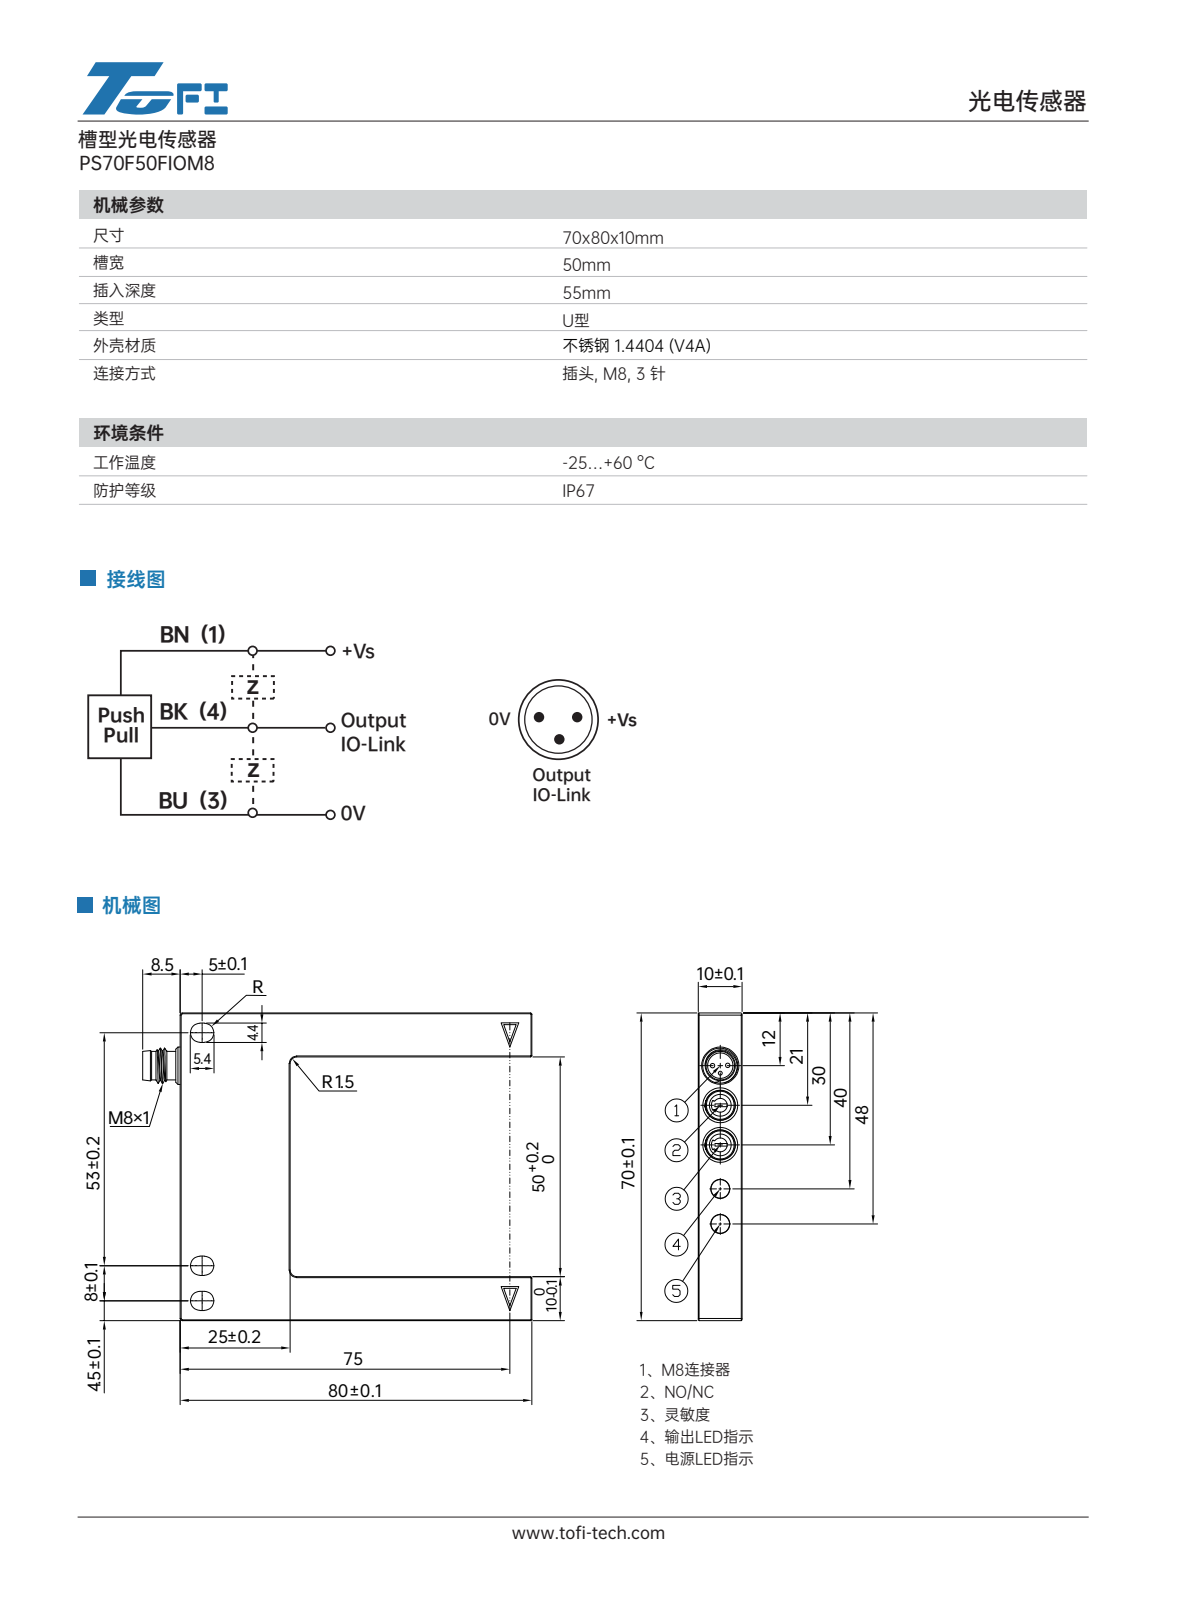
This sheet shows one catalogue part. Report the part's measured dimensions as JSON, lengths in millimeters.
{"part_name": "P70-CP", "step_written_by": "SolidWorks 2016 (CONFIG_CONTROL_DESIGN)", "units": "millimeters", "bodies": {"solids": 0, "faces": 776, "planar": 346, "cylindrical": 232, "other": 198}, "overall_size": [88.5, 70, 10], "round_holes": [[8, 3], [4.33, 2], [5, 2], [5.9, 2], [7.1, 2], [4.04, 1], [5.04, 1], [5.1, 1], [5.8, 1], [5.85, 1], [6.85, 1], [6.9, 1]], "round_bosses_or_shafts": [[0.5, 6], [1, 3], [6.8, 2], [4.3, 2], [2.7, 2], [9, 1], [8, 1], [7.8, 1]], "partial_cylinders_radius": [[2.2, 9], [0.1, 8], [0.3, 4], [0.2, 2], [0.23, 2], [0.23, 2], [0.23, 2], [0.5, 2]], "face_to_face_distances": [10, 60, 70, 50, 25, 80, 55, 4.7, 1.3, 20.3], "hole_center_spacings": [9, 18, 8, 10, 19, 27, 28, 36]}
